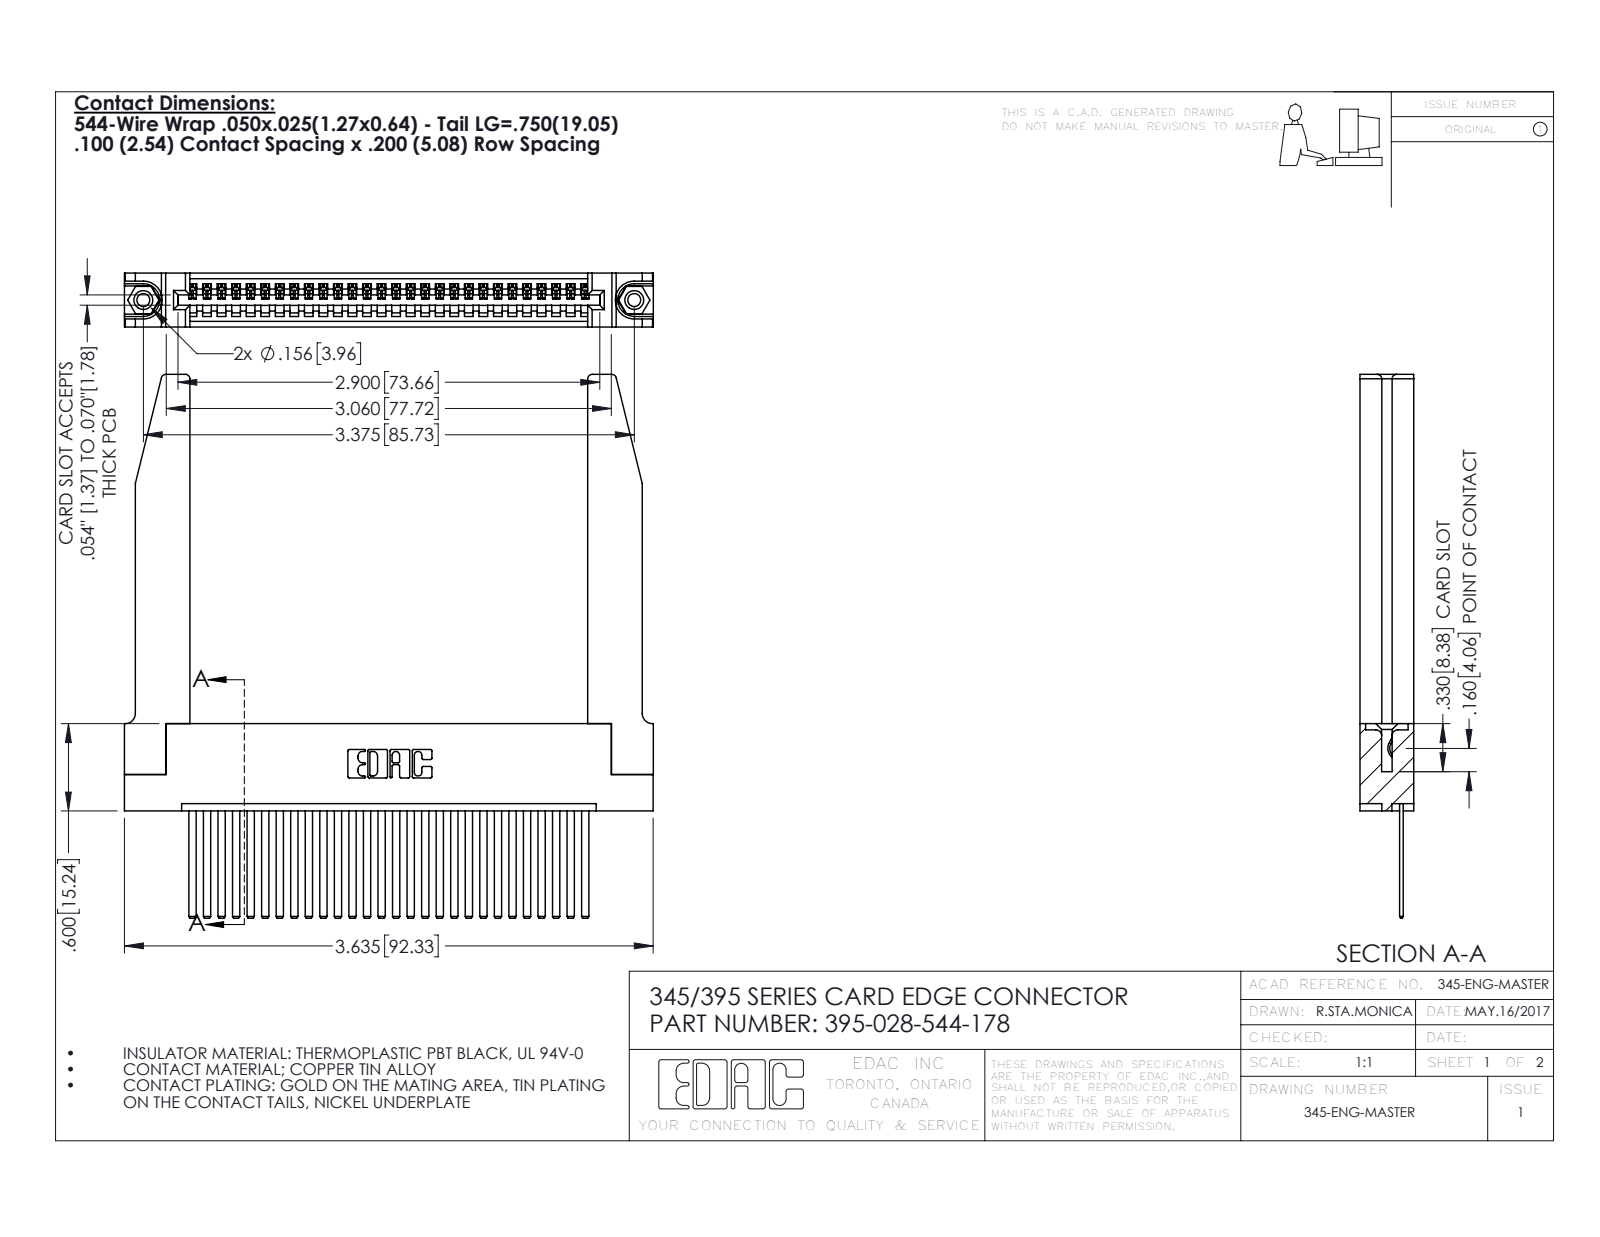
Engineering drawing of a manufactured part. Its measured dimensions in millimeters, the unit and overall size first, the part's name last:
Units: millimetres
Overall size (bounding box): 94.9 × 92.4 × 9.4
Round holes (diameter × count): ⌀2.3 ×2, ⌀3.2 ×2, ⌀4 ×2, ⌀1.6 ×1
Round bosses / shafts (diameter × count): ⌀3.9 ×2
Partial cylindrical surfaces — rounded edges, fillets, slot ends (radius × count): R0.2 ×56, R0.3 ×22, R0.8 ×8, R0.2 ×6, R0.8 ×6, R0.7 ×3, R0.8 ×2, R1 ×2
Main face-to-face distances: 9.4, 1.8, 7.6, 2.5, 6.9, 0.6, 5.1, 3.8, 3.8, 5.7
Hole centre spacings: 6.9, 79.8, 85.7
Volume: 16 750 mm³ · Surface area: 19 560 mm²
Bodies: 33 solids, 1816 faces (1230 planar, 534 cylindrical, 52 other)
Part name (STEP PRODUCT): 345-250-001_345-250-001-102; 395-028-544-178; 345-220-078_345-220-078; 345 Part_Flush Mounting Lugs - 0.156 Dia-TH (+1 more)
STEP written by: SolidWorks 2016 (CONFIG_CONTROL_DESIGN)
